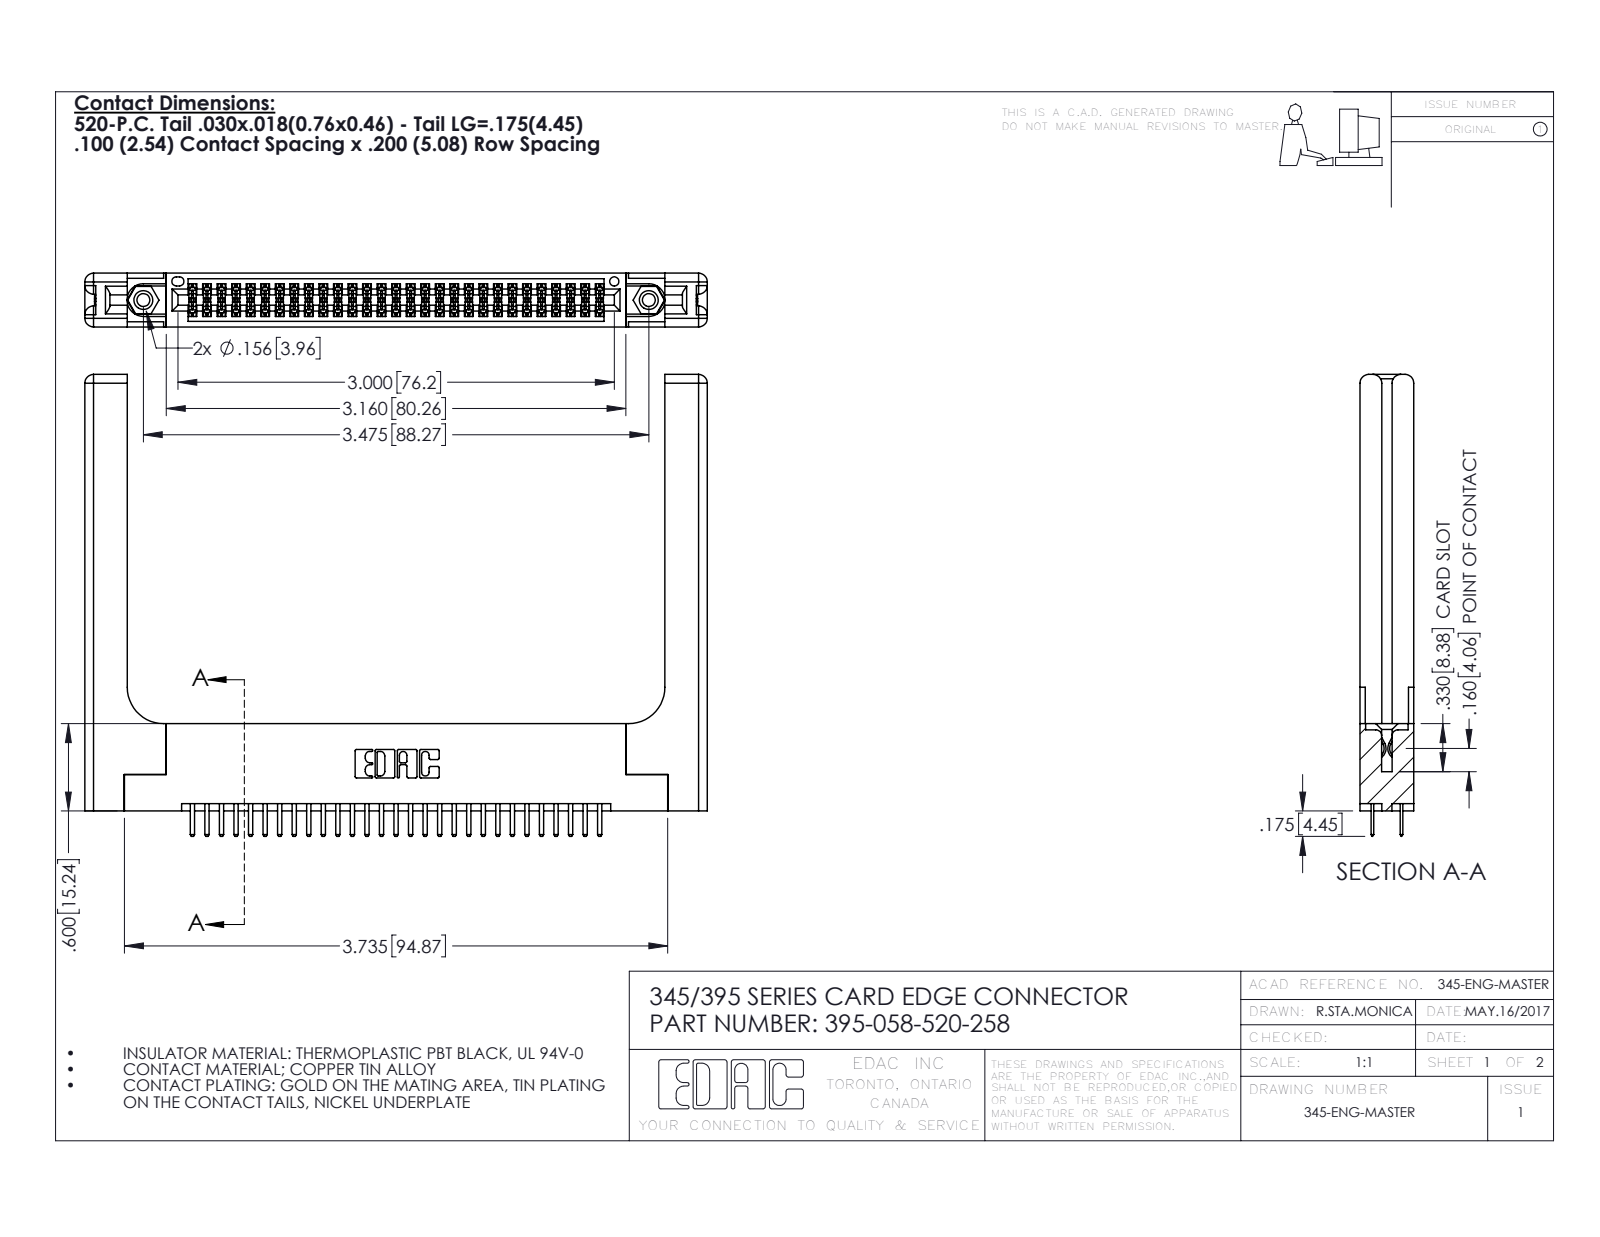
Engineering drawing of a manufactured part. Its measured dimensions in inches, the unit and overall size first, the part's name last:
Units: inches
Overall size (bounding box): 4.279 × 3.175 × 0.37
Round holes (diameter × count): ⌀0.089 ×2, ⌀0.125 ×2, ⌀0.156 ×2, ⌀0.064 ×1
Round bosses / shafts (diameter × count): ⌀0.155 ×2
Partial cylindrical surfaces — rounded edges, fillets, slot ends (radius × count): R0.006 ×87, R0.01 ×62, R0.01 ×22, R0.06 ×16, R0.007 ×6, R0.031 ×6, R0.026 ×3, R0.014 ×2
Main face-to-face distances: 0.37, 0.072, 0.298, 0.2, 0.148, 0.15, 0.098, 0.272, 0.025, 0.225
Hole centre spacings: 0.27, 3.24, 3.475
Volume: 1.153 in³ · Surface area: 31.22 in²
Bodies: 63 solids, 3514 faces (2258 planar, 1196 cylindrical, 60 other)
Part name (STEP PRODUCT): 345 Part_Flush Mounting Lugs - 0.156 Dia-TH; 345-250-001_345-250-001-102; 395-058-520-258; 345-292-001_345-293-120 (+1 more)
STEP written by: SolidWorks 2016 (CONFIG_CONTROL_DESIGN)
